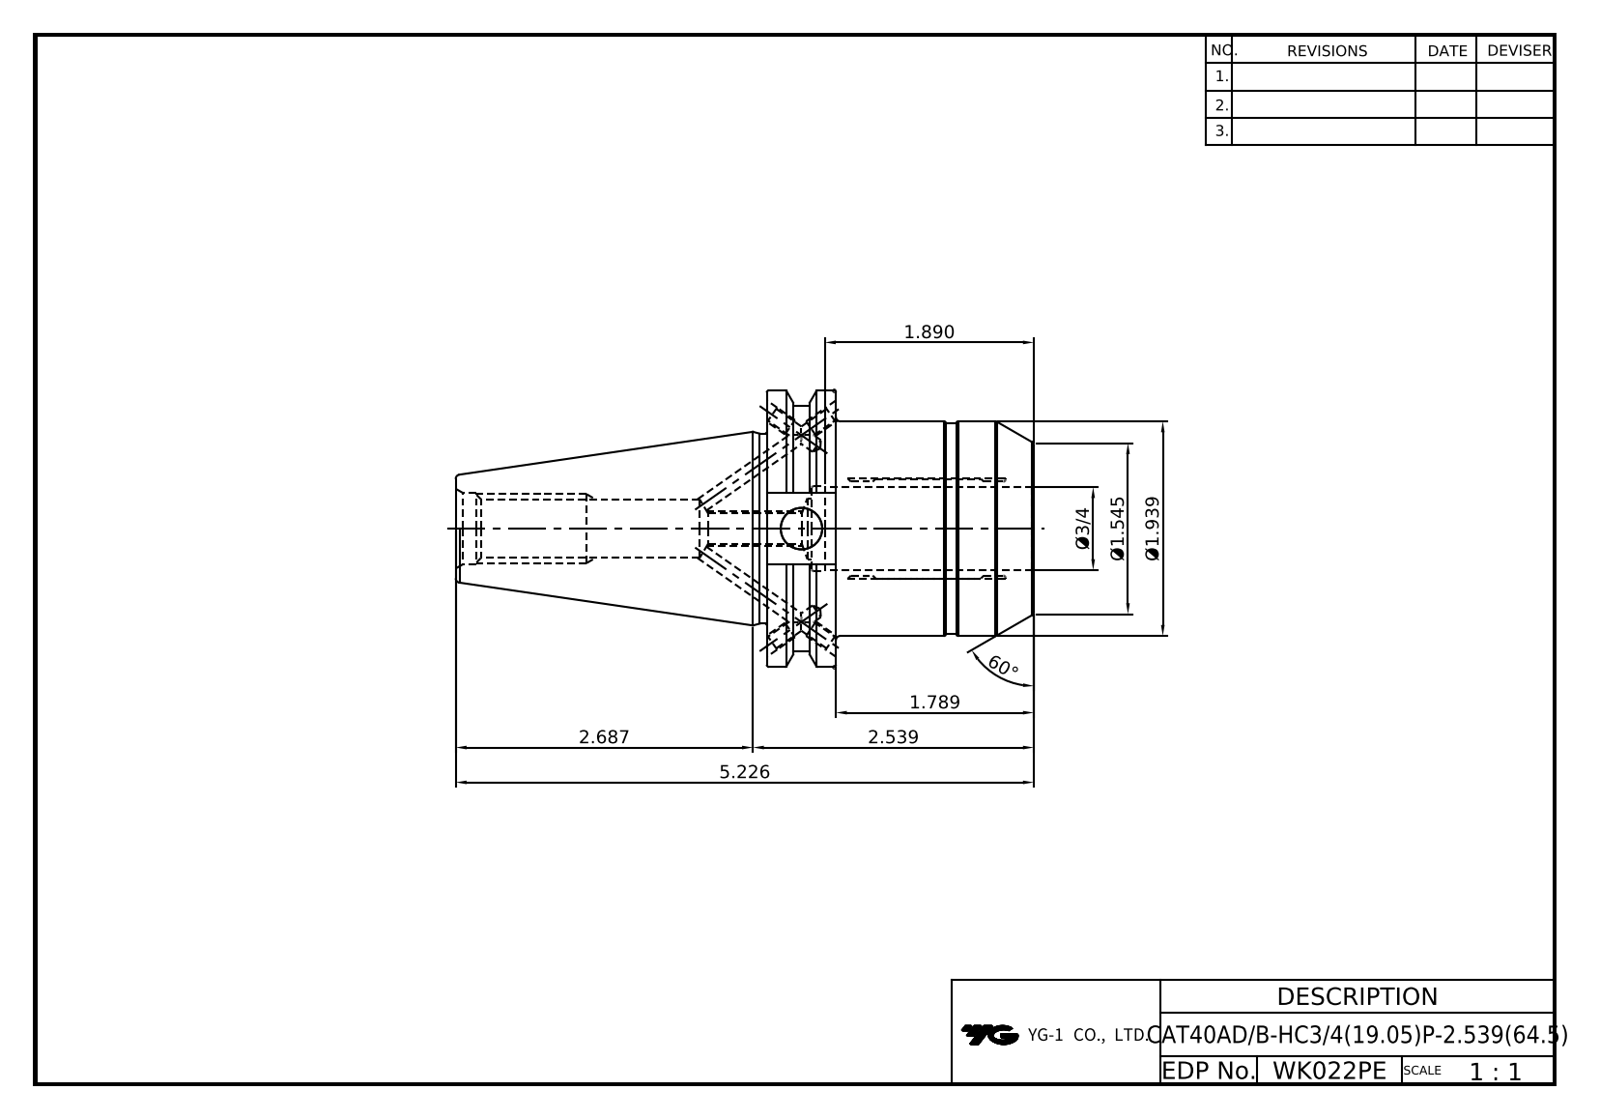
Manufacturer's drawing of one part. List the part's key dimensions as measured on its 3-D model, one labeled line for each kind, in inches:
Part name (STEP PRODUCT): LO-CAT40ADB-HC19.05P-64.5
STEP written by: Autodesk Inventor 2025 (AUTOMOTIVE_DESIGN)
Units: inches
Bodies: 1 solid, 83 faces (31 planar, 30 cylindrical, 22 other)
Overall size (bounding box): 5.226 × 2.5 × 2.405
Volume: 10.48 in³ · Surface area: 46.62 in²
Round holes (diameter × count): ⌀0.128 ×4, ⌀0.157 ×4, ⌀0.272 ×1, ⌀0.375 ×1, ⌀0.527 ×1, ⌀0.551 ×1, ⌀0.642 ×1, ⌀0.75 ×1, ⌀0.781 ×1
Round bosses / shafts (diameter × count): ⌀2.5 ×1, ⌀2.217 ×1, ⌀1.939 ×1, ⌀1.9 ×1, ⌀1.717 ×1
Partial cylindrical surfaces — rounded edges, fillets, slot ends (radius × count): R0.322 ×1
Main face-to-face distances: 2.415, 0.625, 1.789, 1.874, 0.645, 2.812, 3.437, 5.226, 3.219, 0.407
Hole centre spacings: 1.383
